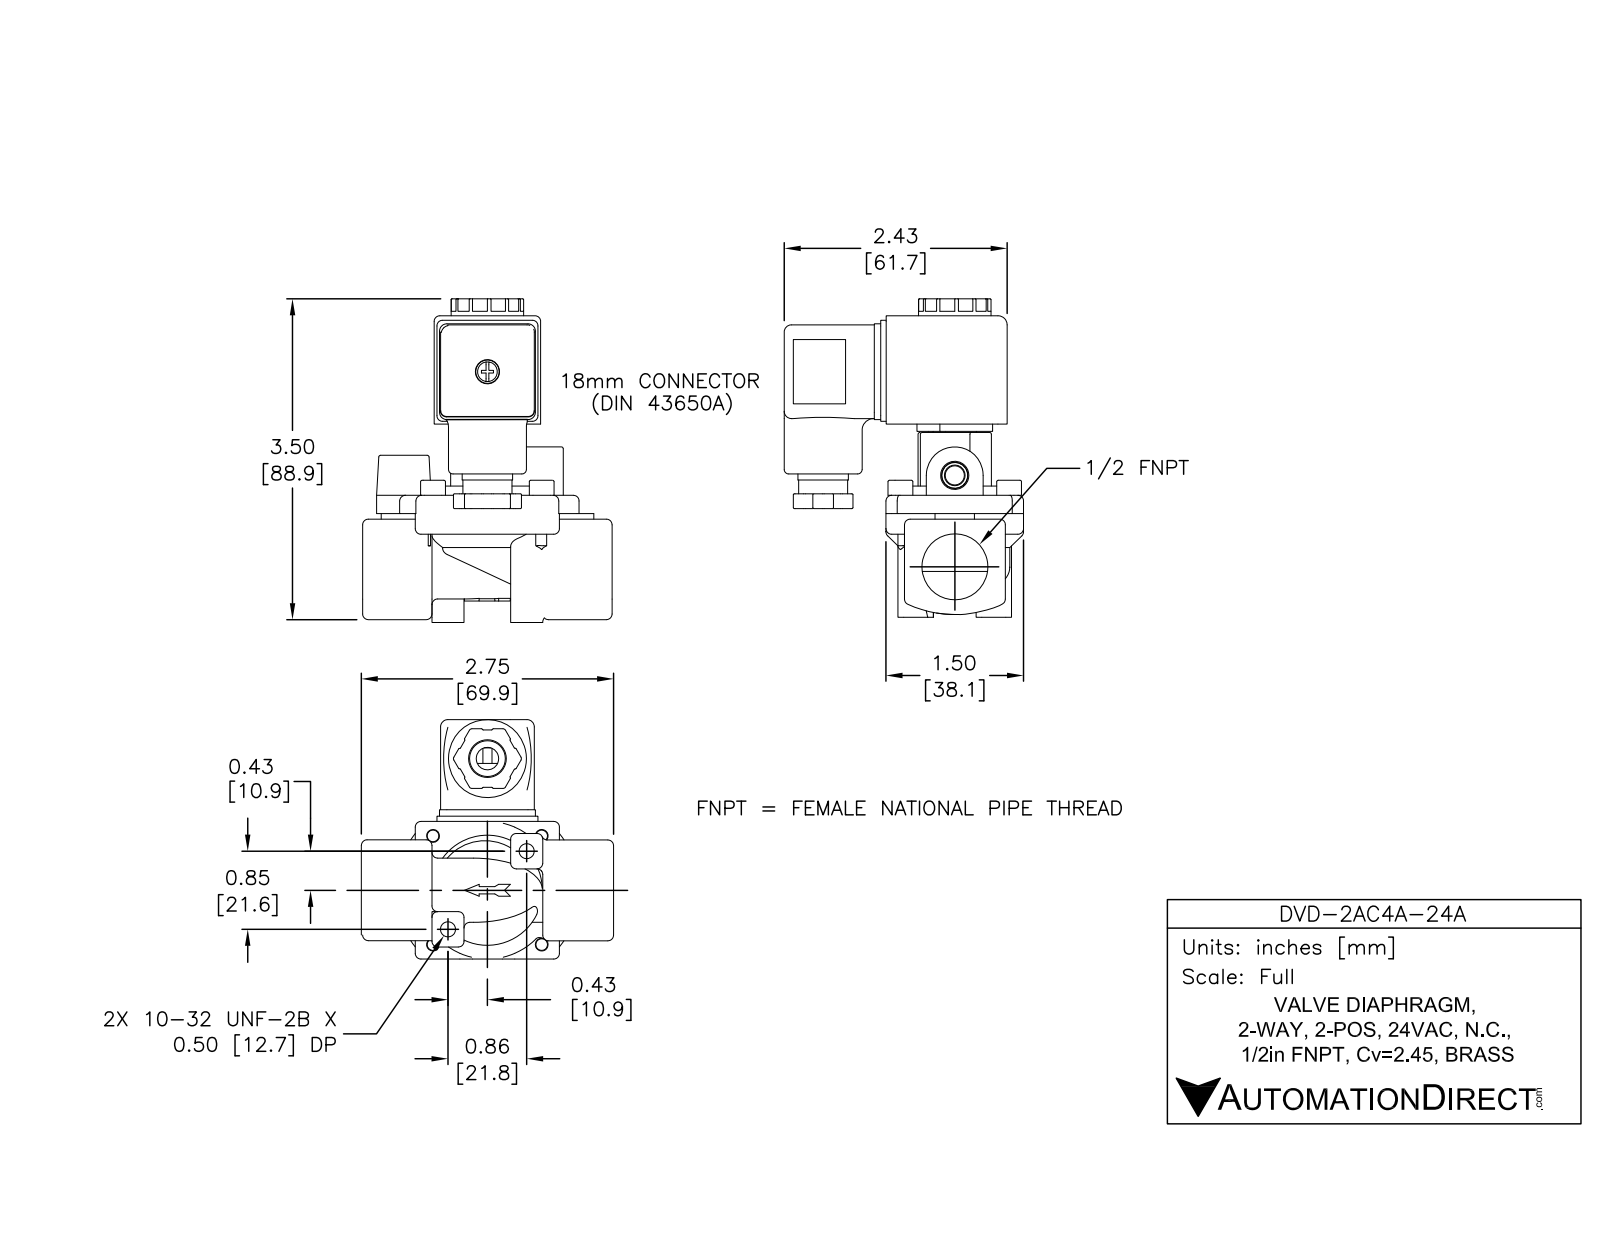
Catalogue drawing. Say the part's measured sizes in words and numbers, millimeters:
The part is named "DVD-2AC4A-24A". Its 3-D file was written by "SolidWorks 2015 (AUTOMOTIVE_DESIGN)". It is 9 solids with 1878 faces: 872 planar, 415 cylindrical and 591 other. Overall it measures 88.2 by 69.1 by 66.3 millimeters. Its volume is 92 240 cubic millimeters and its surface area 44 350 square millimeters. Round holes: 6 of diameter 4.2, 4 of diameter 3.5, 2 of diameter 1.5, 2 of diameter 2.5, 2 of diameter 3.6, 2 of diameter 11, 2 of diameter 17.9, 1 of diameter 1.6, 1 of diameter 2, 1 of diameter 2.3, 1 of diameter 2.4, 1 of diameter 2.6. Round bosses or shafts: 4 of diameter 6.9, 4 of diameter 4.5, 4 of diameter 4.1, 1 of diameter 34.9, 1 of diameter 21.6, 1 of diameter 20.1, 1 of diameter 15.5, 1 of diameter 15. Partial cylindrical surfaces (rounded edges, fillets, slot ends): 52 of radius 0.3, 22 of radius 1.6, 21 of radius 1.6, 14 of radius 1.6, 12 of radius 2, 12 of radius 4, 8 of radius 1.3, 6 of radius 0.8. The main face-to-face distances are 23.5, 5.1, 29.5, 30, 26.3, 27.9, 2, 1.5, 24.3, 33. The hole center spacings are 21.3, 23.5, 23.5, 30.1, 11.4, 19.8, 31.2, 5.9.
